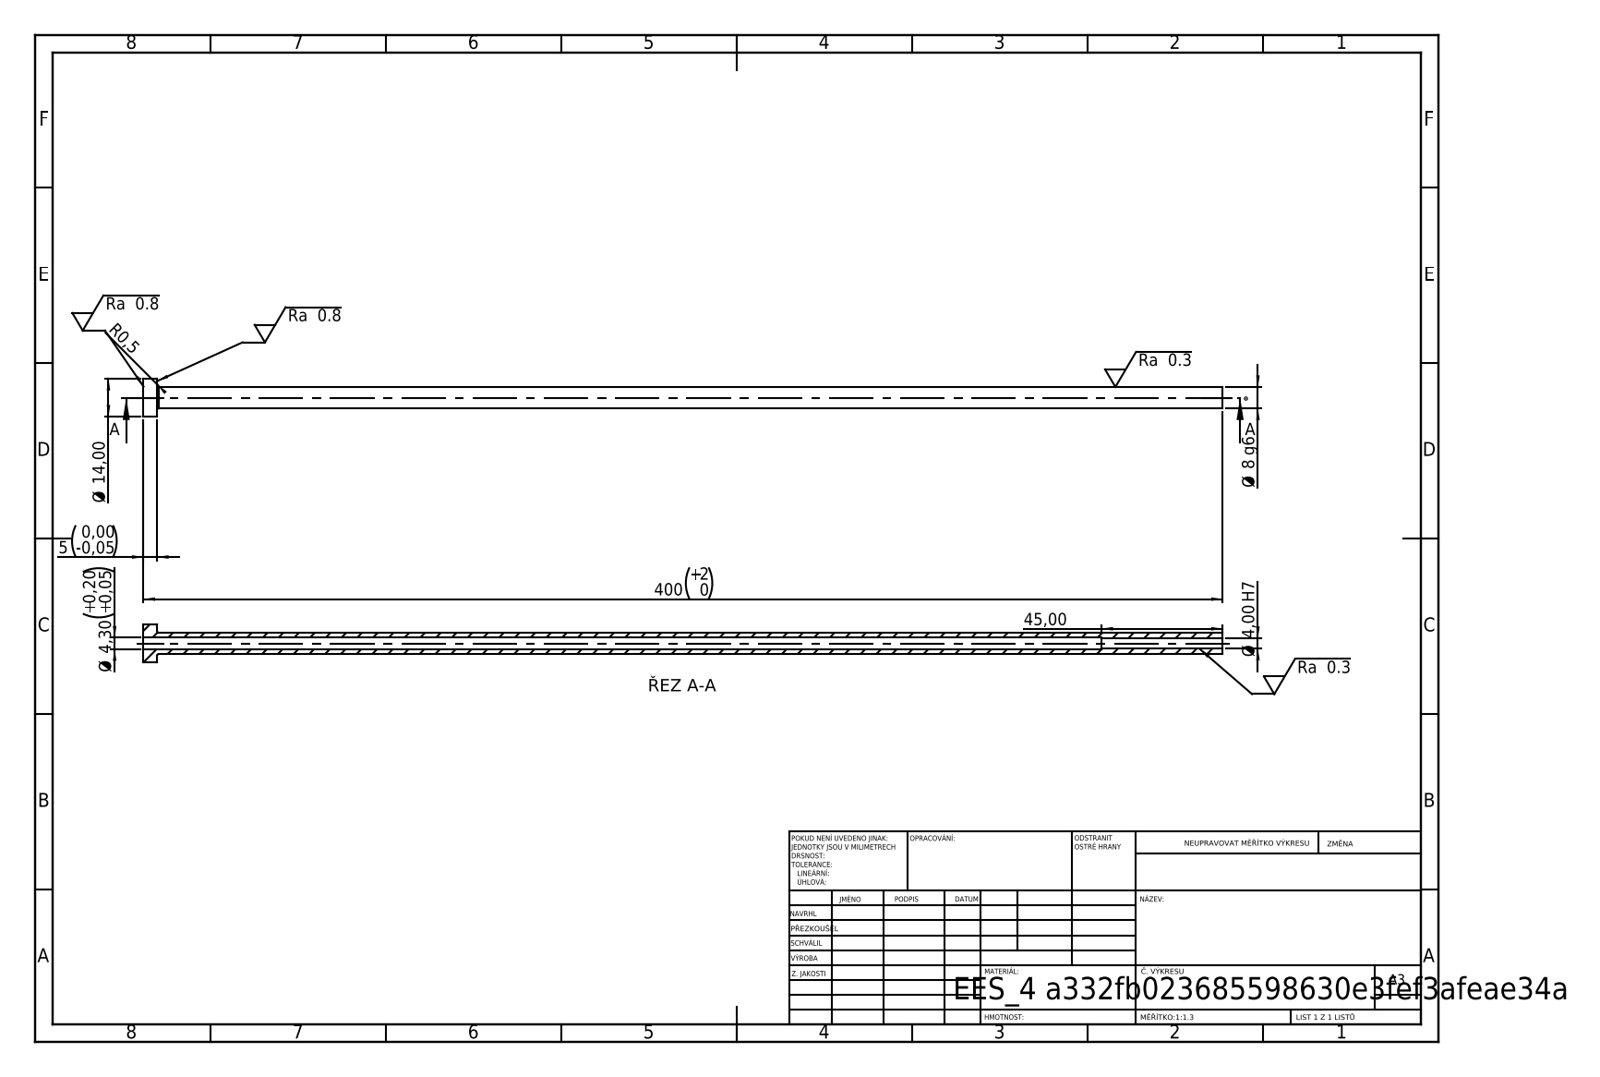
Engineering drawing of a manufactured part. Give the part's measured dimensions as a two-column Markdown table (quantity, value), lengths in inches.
| quantity | value |
| --- | --- |
| STEP written by | SolidWorks 2019 (CONFIG_CONTROL_DESIGN) |
| units | inches |
| bodies | 1 solid, 14 faces (4 planar, 8 cylindrical, 2 other) |
| overall size | 15.748 × 0.551 × 0.551 |
| volume | 0.91 in³ |
| surface area | 24.47 in² |
| round holes (diameter × count) | 0.157 × 1, 0.169 × 1 |
| round bosses / shafts (diameter × count) | 0.551 × 1, 0.315 × 1 |
| main face-to-face distances | 0.197, 15.748, 15.551, 13.976, 13.78, 1.772 |
